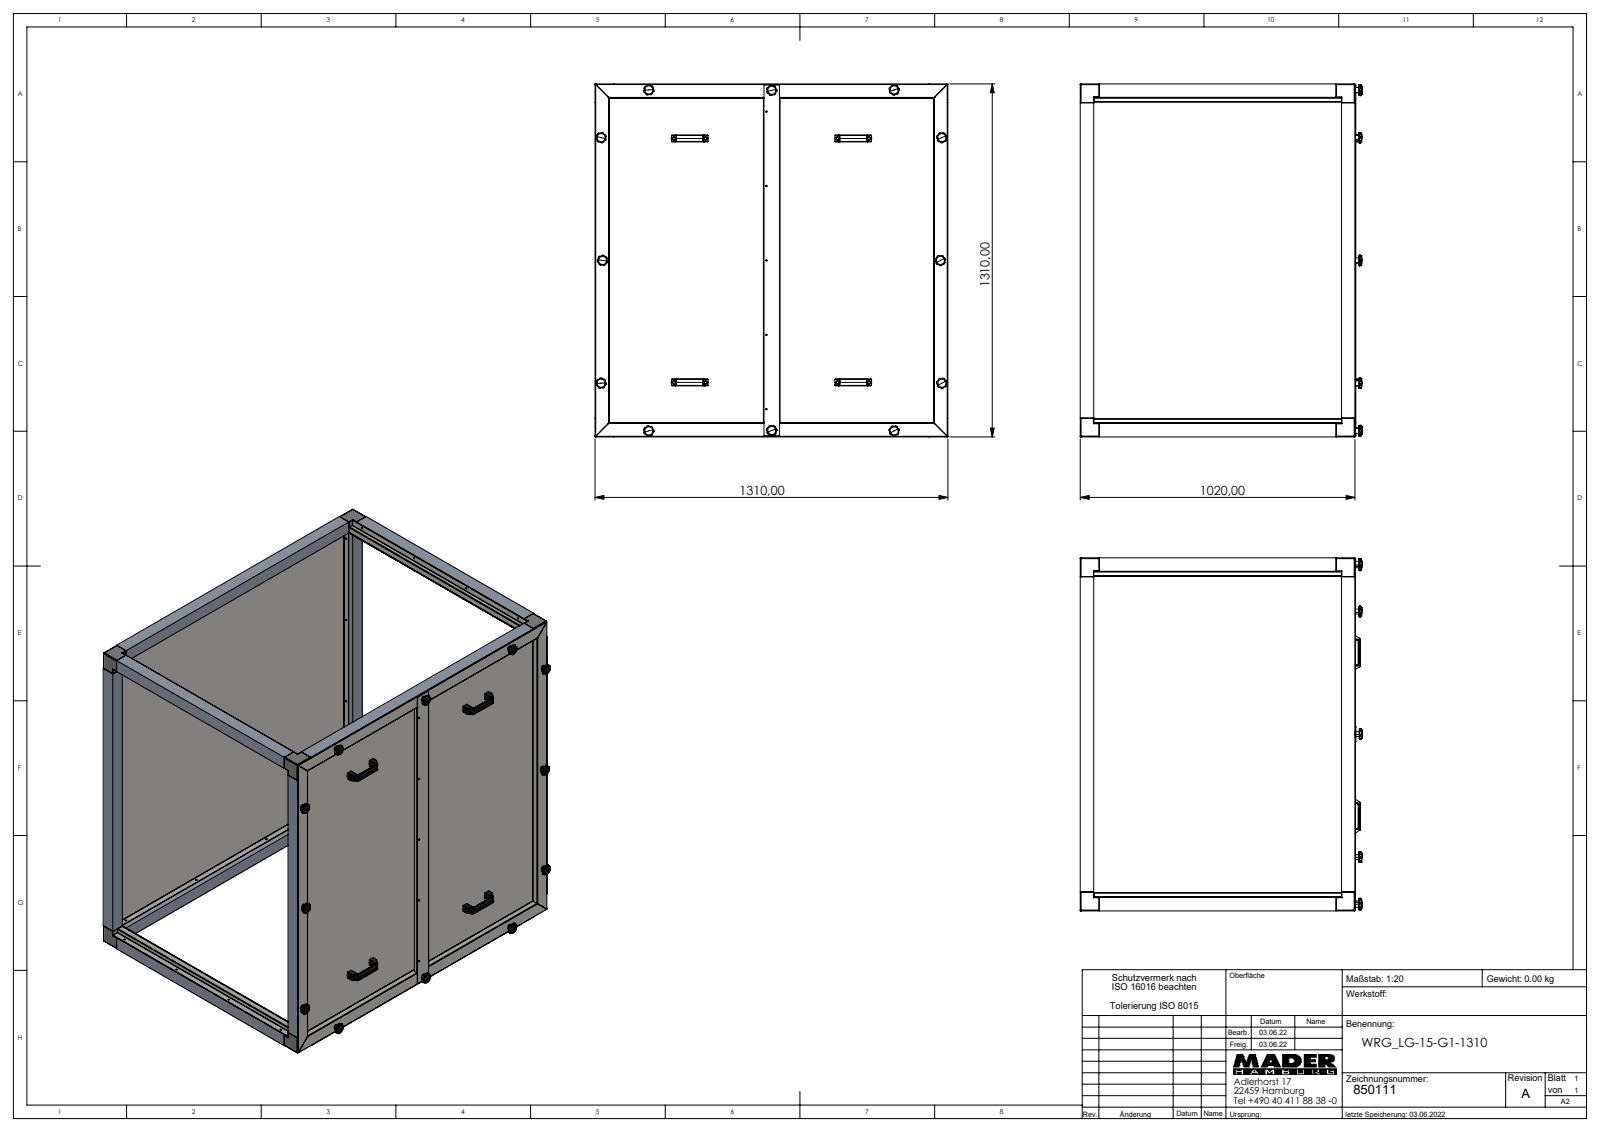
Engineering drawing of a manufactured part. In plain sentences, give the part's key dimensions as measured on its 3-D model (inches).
The part is named "850111_LG-15-G1-1310". Its 3-D file was written by "SolidWorks 2019 (CONFIG_CONTROL_DESIGN)". It is 48 solids with 4202 faces: 2088 planar, 1398 cylindrical and 716 other. Overall it measures 51.575 by 51.575 by 41.26 inches. Its volume is 775.6 cubic inches and its surface area 22 380 square inches. Round holes: 45 of diameter 0.197, 16 of diameter 0.165, 10 of diameter 0.118, 10 of diameter 0.512, 8 of diameter 0.236, 8 of diameter 0.335, 8 of diameter 0.354, 8 of diameter 0.531, 2 of diameter 0.472. Round bosses or shafts: 12 of diameter 0.315. Partial cylindrical surfaces (rounded edges, fillets, slot ends): 216 of radius 0.079, 84 of radius 0.197, 84 of radius 0.591, 42 of radius 0.029, 42 of radius 0.088, 28 of radius 0.118, 24 of radius 0.039, 4 of radius 0.098. The main face-to-face distances are 0.059, 39.035, 0.079, 1.89, 49.606, 39.094, 38.976, 1.969, 1.811, 38.189. The hole center spacings are 10.761, 50.509, 10.118, 21.522, 51.643, 20.236, 54.904, 51.626.
